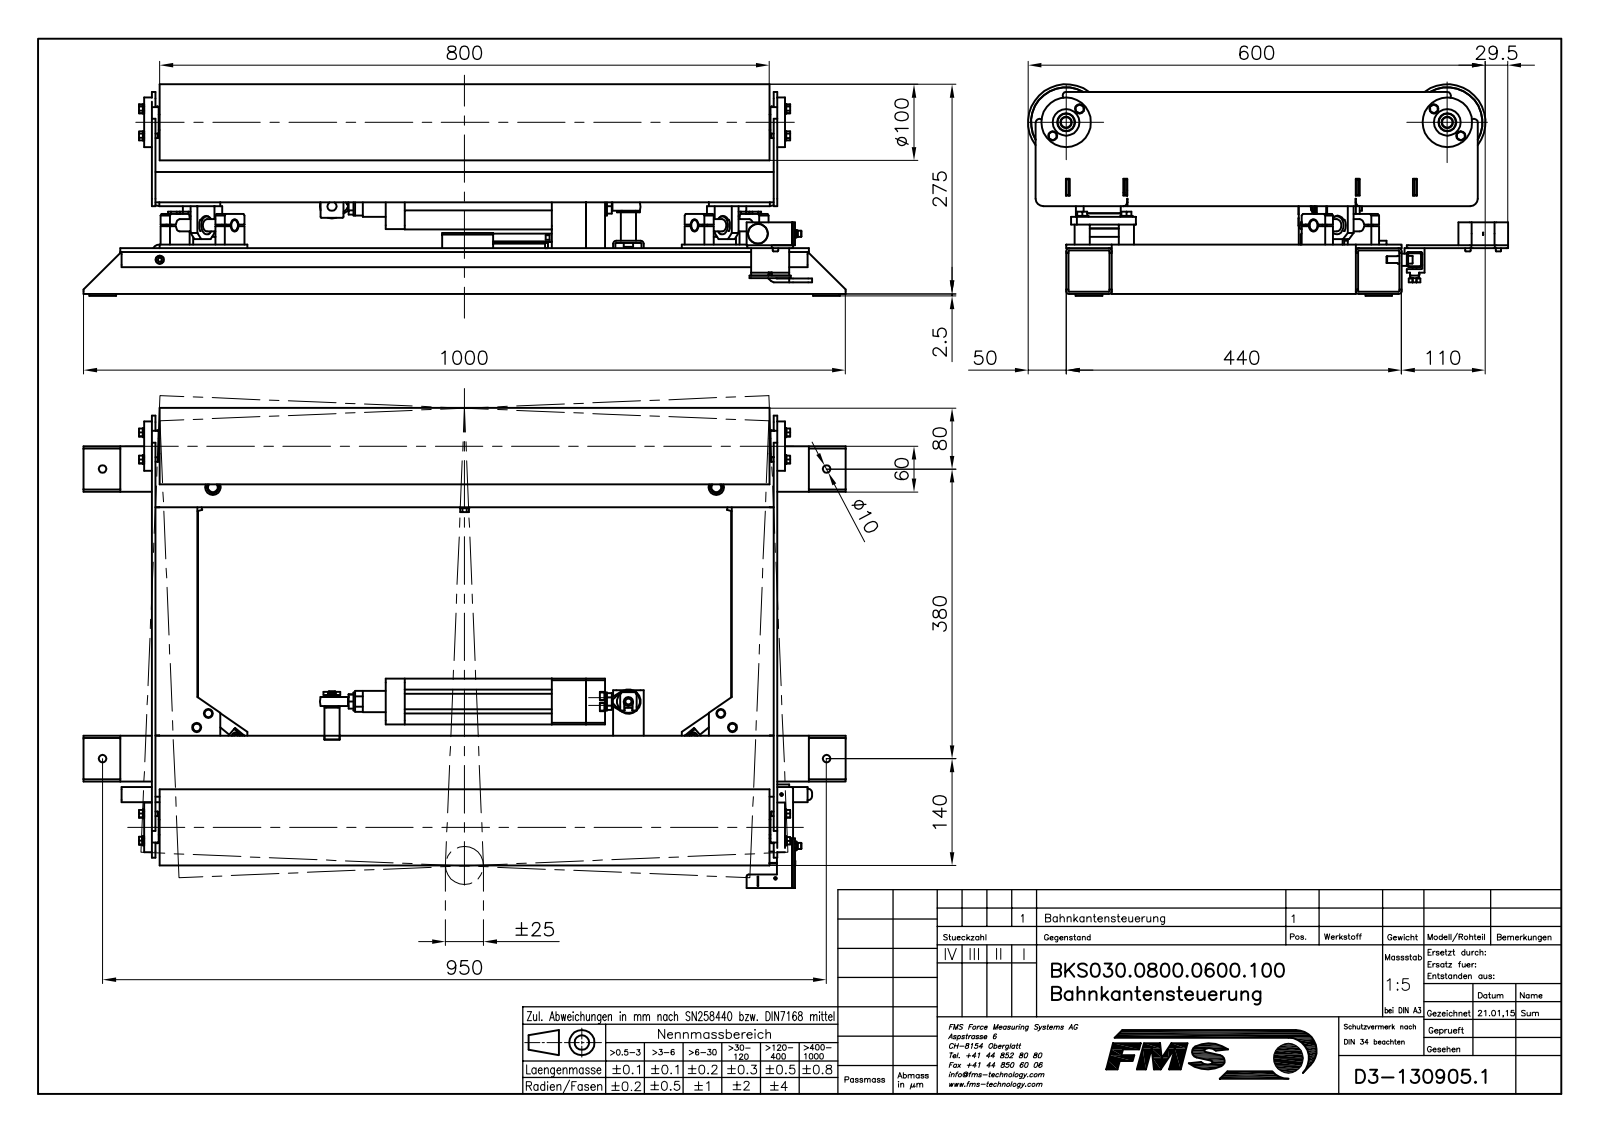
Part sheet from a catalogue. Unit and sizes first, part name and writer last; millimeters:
Units: millimetres
Overall size (bounding box): 1000 × 629.5 × 277.5
Round holes (diameter × count): ⌀5.15 ×19, ⌀7 ×15, ⌀4.3 ×12, ⌀0.99 ×10, ⌀8.4 ×10, ⌀11 ×10, ⌀6.4 ×9, ⌀10 ×8, ⌀0.79 ×6, ⌀3.42 ×6, ⌀6 ×6, ⌀16 ×6
Round bosses / shafts (diameter × count): ⌀6 ×21, ⌀10 ×14, ⌀8 ×13, ⌀12 ×11, ⌀16 ×10, ⌀4 ×10, ⌀20 ×8, ⌀7 ×6
Partial cylindrical surfaces — rounded edges, fillets, slot ends (radius × count): R1 ×30, R4 ×20, R2 ×17, R5 ×13, R0.15 ×10, R8 ×8, R10 ×6, R0.18 ×5
Main face-to-face distances: 3, 57, 60, 5, 380, 37, 120, 157, 100, 63
Hole centre spacings: 47, 2.54, 52.77, 43.66, 11.77, 24.01, 25, 56.68
Volume: 7 567 000 mm³ · Surface area: 3 775 000 mm²
Bodies: 653 solids, 7517 faces (4958 planar, 1810 cylindrical, 749 other)
Part name (STEP PRODUCT): K1309051; K1309052; K1309055; K1309056 (+8 more)
STEP written by: Mechanical Desktop 2009 (CONFIG_CONTROL_DESIGN)
